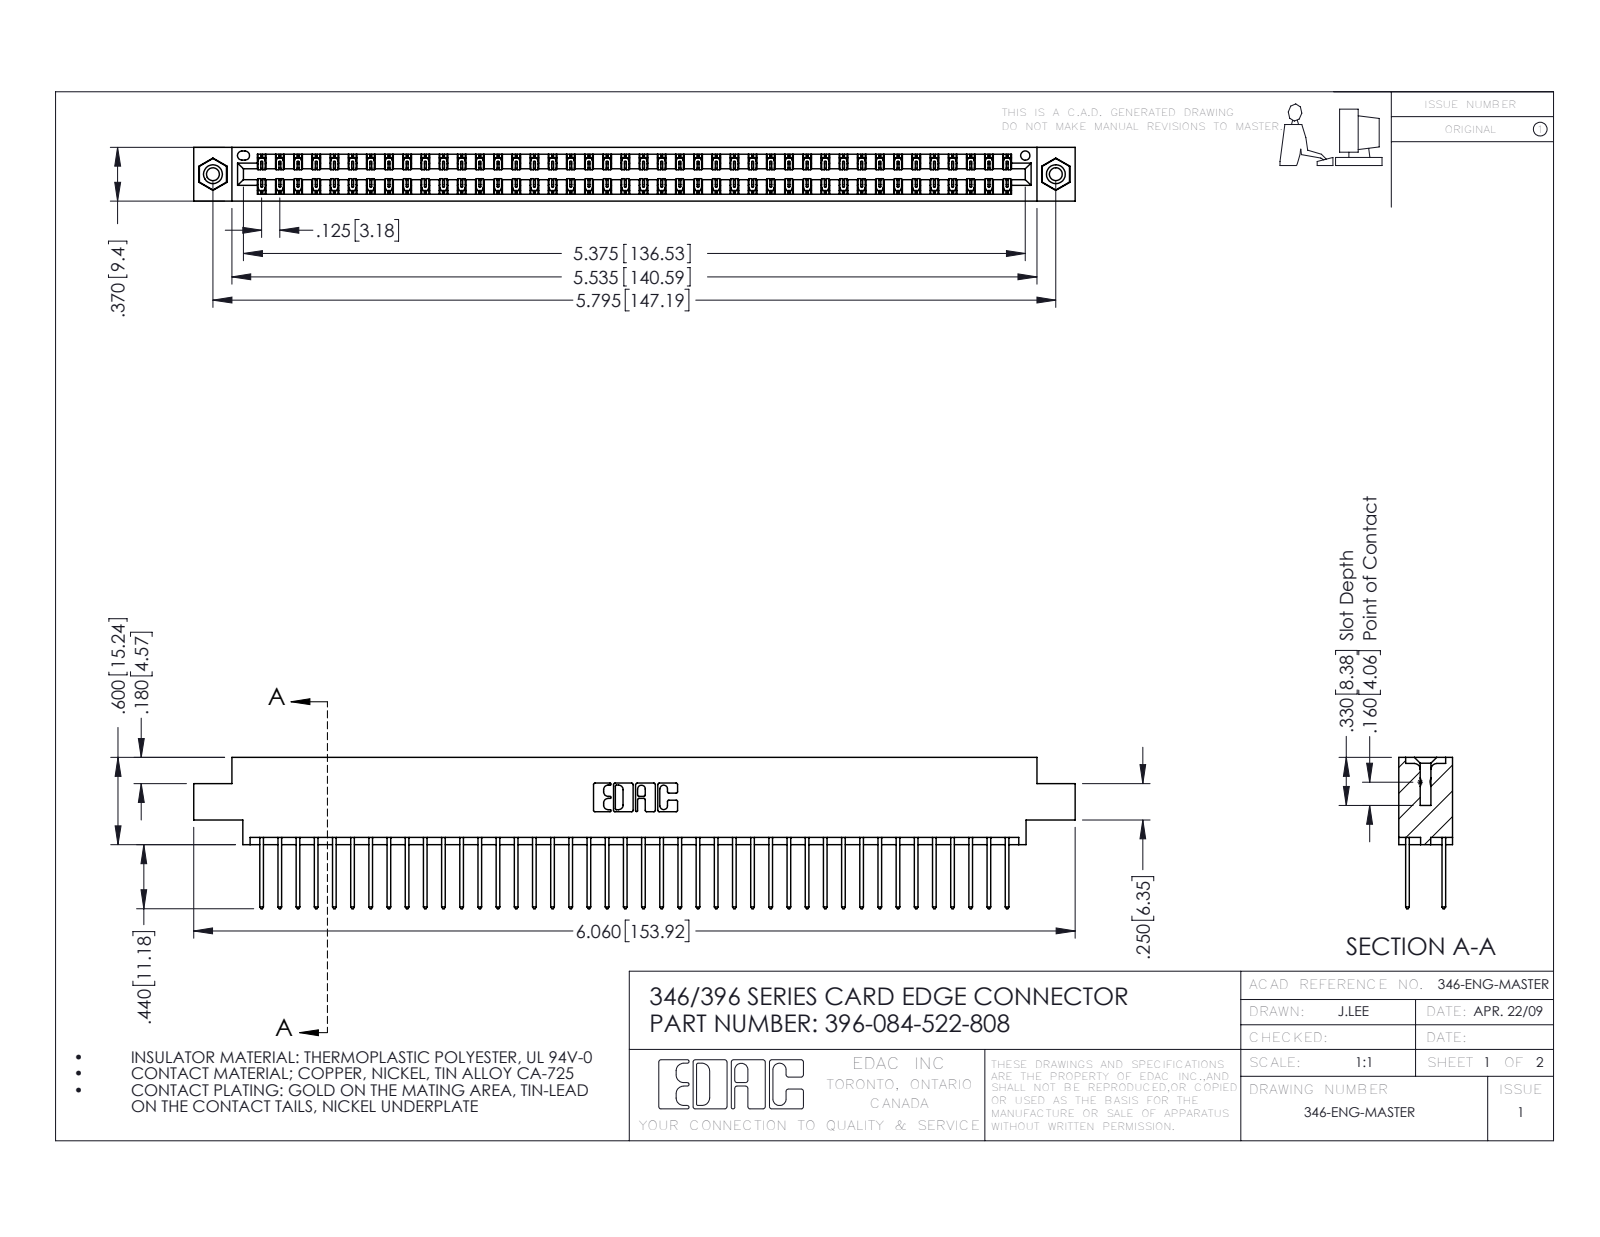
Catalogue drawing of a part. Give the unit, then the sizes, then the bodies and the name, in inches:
Units: inches
Overall size (bounding box): 6.06 × 1.04 × 0.37
Round holes (diameter × count): ⌀0.089 ×2, ⌀0.125 ×2, ⌀0.156 ×2, ⌀0.064 ×1
Round bosses / shafts (diameter × count): ⌀0.155 ×2
Partial cylindrical surfaces — rounded edges, fillets, slot ends (radius × count): R0.006 ×126, R0.01 ×84, R0.01 ×22, R0.007 ×6, R0.031 ×6, R0.026 ×3, R0.014 ×2, R0.022 ×2
Main face-to-face distances: 0.048, 0.322, 0.25, 0.37, 0.072, 0.298, 0.025, 0.275, 0.222, 0.148
Hole centre spacings: 0.246, 5.586, 5.795
Volume: 0.919 in³ · Surface area: 33.95 in²
Bodies: 87 solids, 4554 faces (3052 planar, 1486 cylindrical, 16 other)
Part name (STEP PRODUCT): 345-250-001_345-250-003-102; 345-292-001_345-293-122; 396-084-522-808; 346 Part_0.170 Offset - 0.156 Dia-TI
STEP written by: SolidWorks 2016 (CONFIG_CONTROL_DESIGN)
